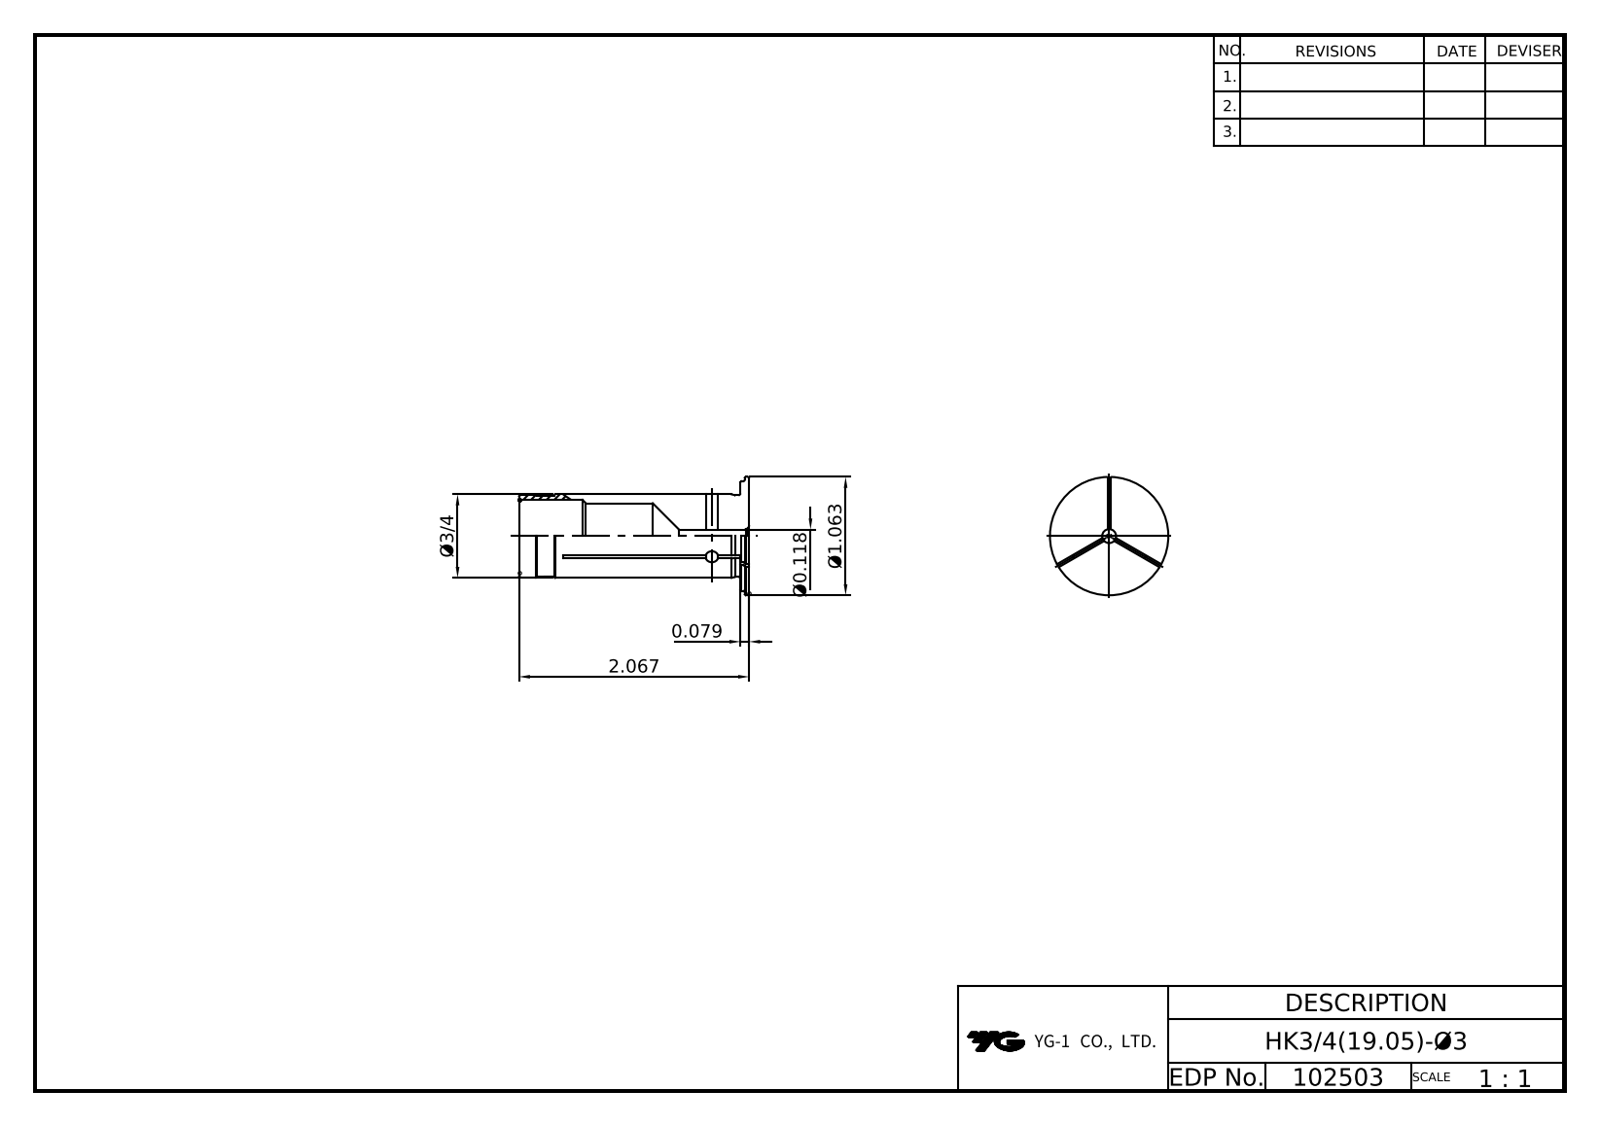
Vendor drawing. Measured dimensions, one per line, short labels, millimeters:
name: LO-HK19.05-3
written by: Autodesk Inventor 2025 (AP242_MANAGED_MODEL_BASED_3D_ENGINEERING_MIM_LF)
unit: mm
bodies: 1 solid, 12 faces (4 planar, 6 cylindrical, 2 other)
size: 52.5 × 27 × 27
volume: 8 964 mm³; area: 6 023 mm²
holes: 1× ⌀3, 1× ⌀15, 1× ⌀16.5
bosses: 1× ⌀27, 1× ⌀25, 1× ⌀19.05
face distances: 2, 1, 50.5, 51.5, 52.5
